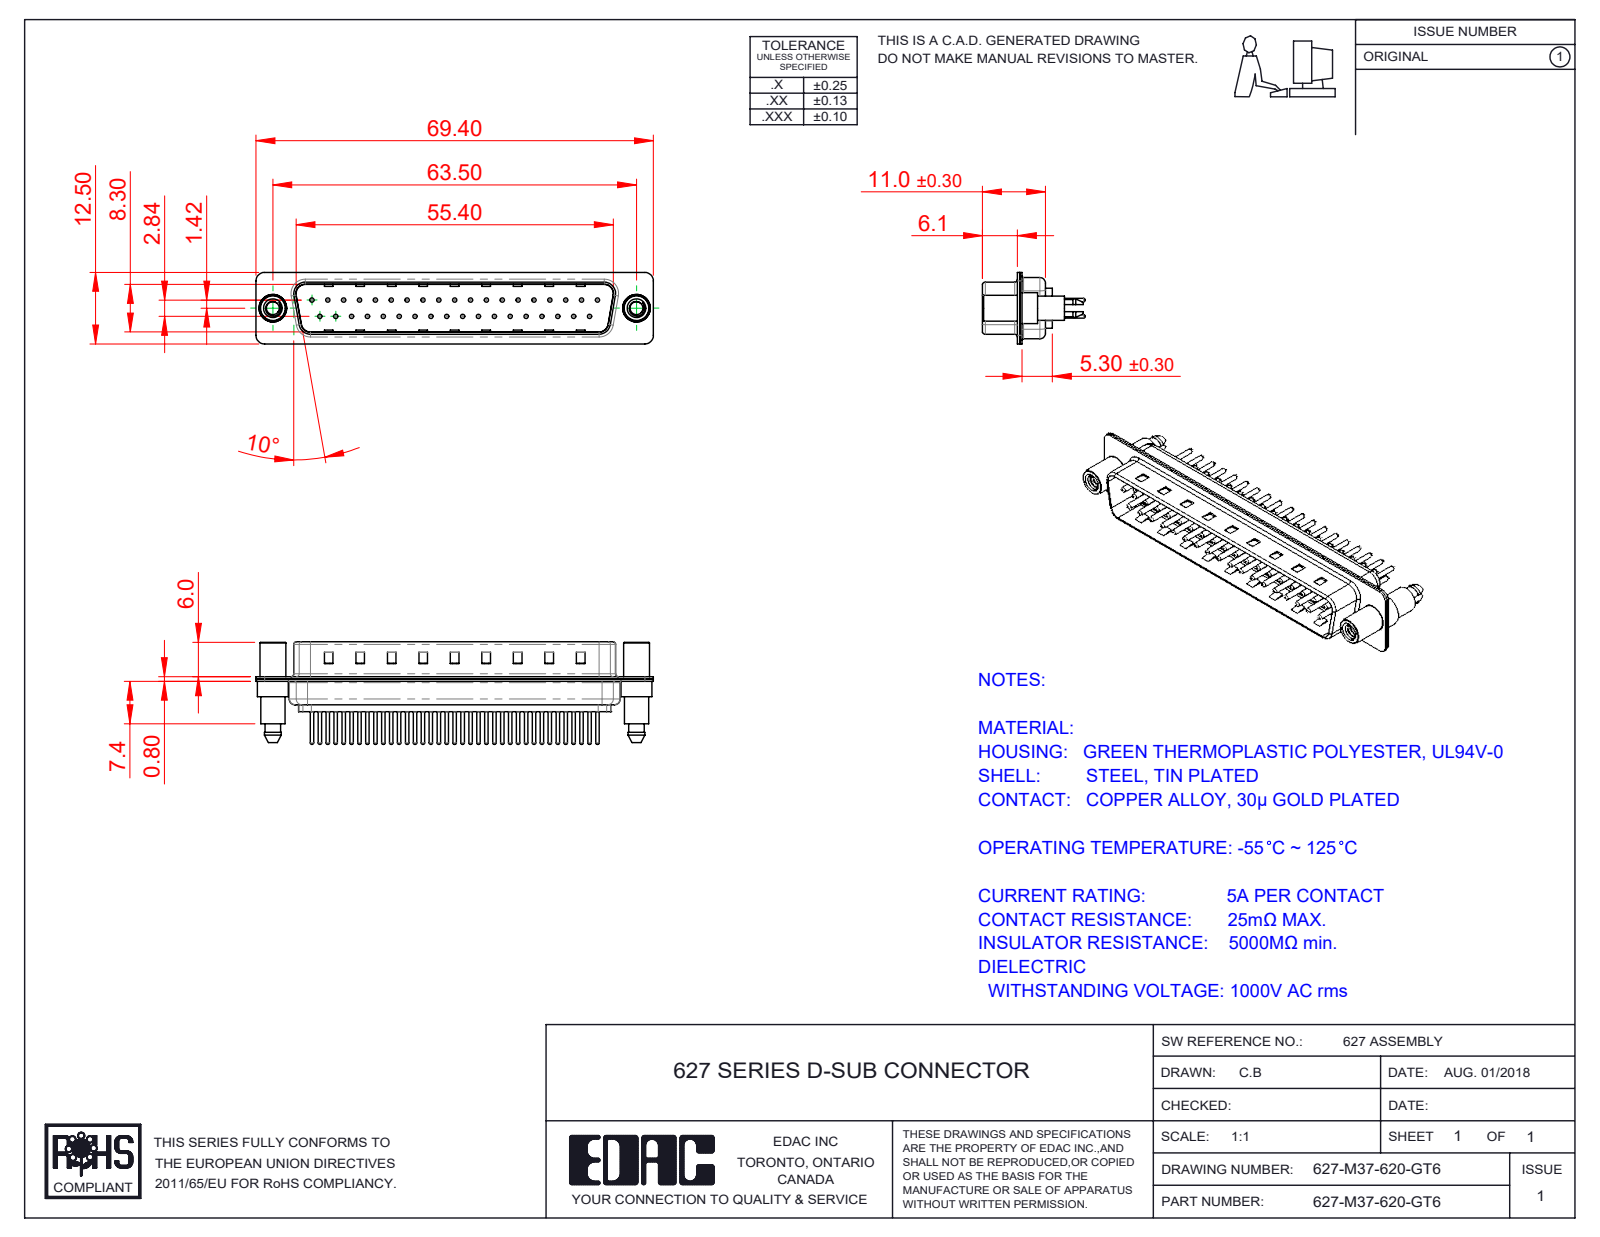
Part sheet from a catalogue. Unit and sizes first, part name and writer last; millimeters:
Units: millimetres
Overall size (bounding box): 69.4 × 17.9 × 12.5
Round holes (diameter × count): ⌀0.75 ×37, ⌀1.6 ×37, ⌀2 ×37, ⌀2.26 ×2, ⌀4 ×2, ⌀4.8 ×2
Round bosses / shafts (diameter × count): ⌀1.5 ×37, ⌀0.6 ×37, ⌀5.4 ×2, ⌀4.9 ×2, ⌀4.5 ×2, ⌀4.25 ×2
Partial cylindrical surfaces — rounded edges, fillets, slot ends (radius × count): R1.5 ×18, R2 ×12, R1.6 ×10, R0.5 ×8, R0.25 ×4, R0.6 ×4, R0.65 ×4, R0.9 ×4
Main face-to-face distances: 0.4, 0.8, 9.5, 9.1, 8.7, 9.9, 1.2, 5.7, 0.75, 0.35
Hole centre spacings: 2.77, 5.54, 3.16, 8.31, 11.08, 13.85, 16.62, 19.39
Volume: 4 106 mm³ · Surface area: 9 737 mm²
Bodies: 42 solids, 1833 faces (480 planar, 687 cylindrical, 666 other)
Part name (STEP PRODUCT): 627M Shell Front_37 Contacts; 627M Contact Row 1_20; 627M Housing_37 Contacts; 627-M37-620-GT6 (+3 more)
STEP written by: SolidWorks 2020 (CONFIG_CONTROL_DESIGN)
